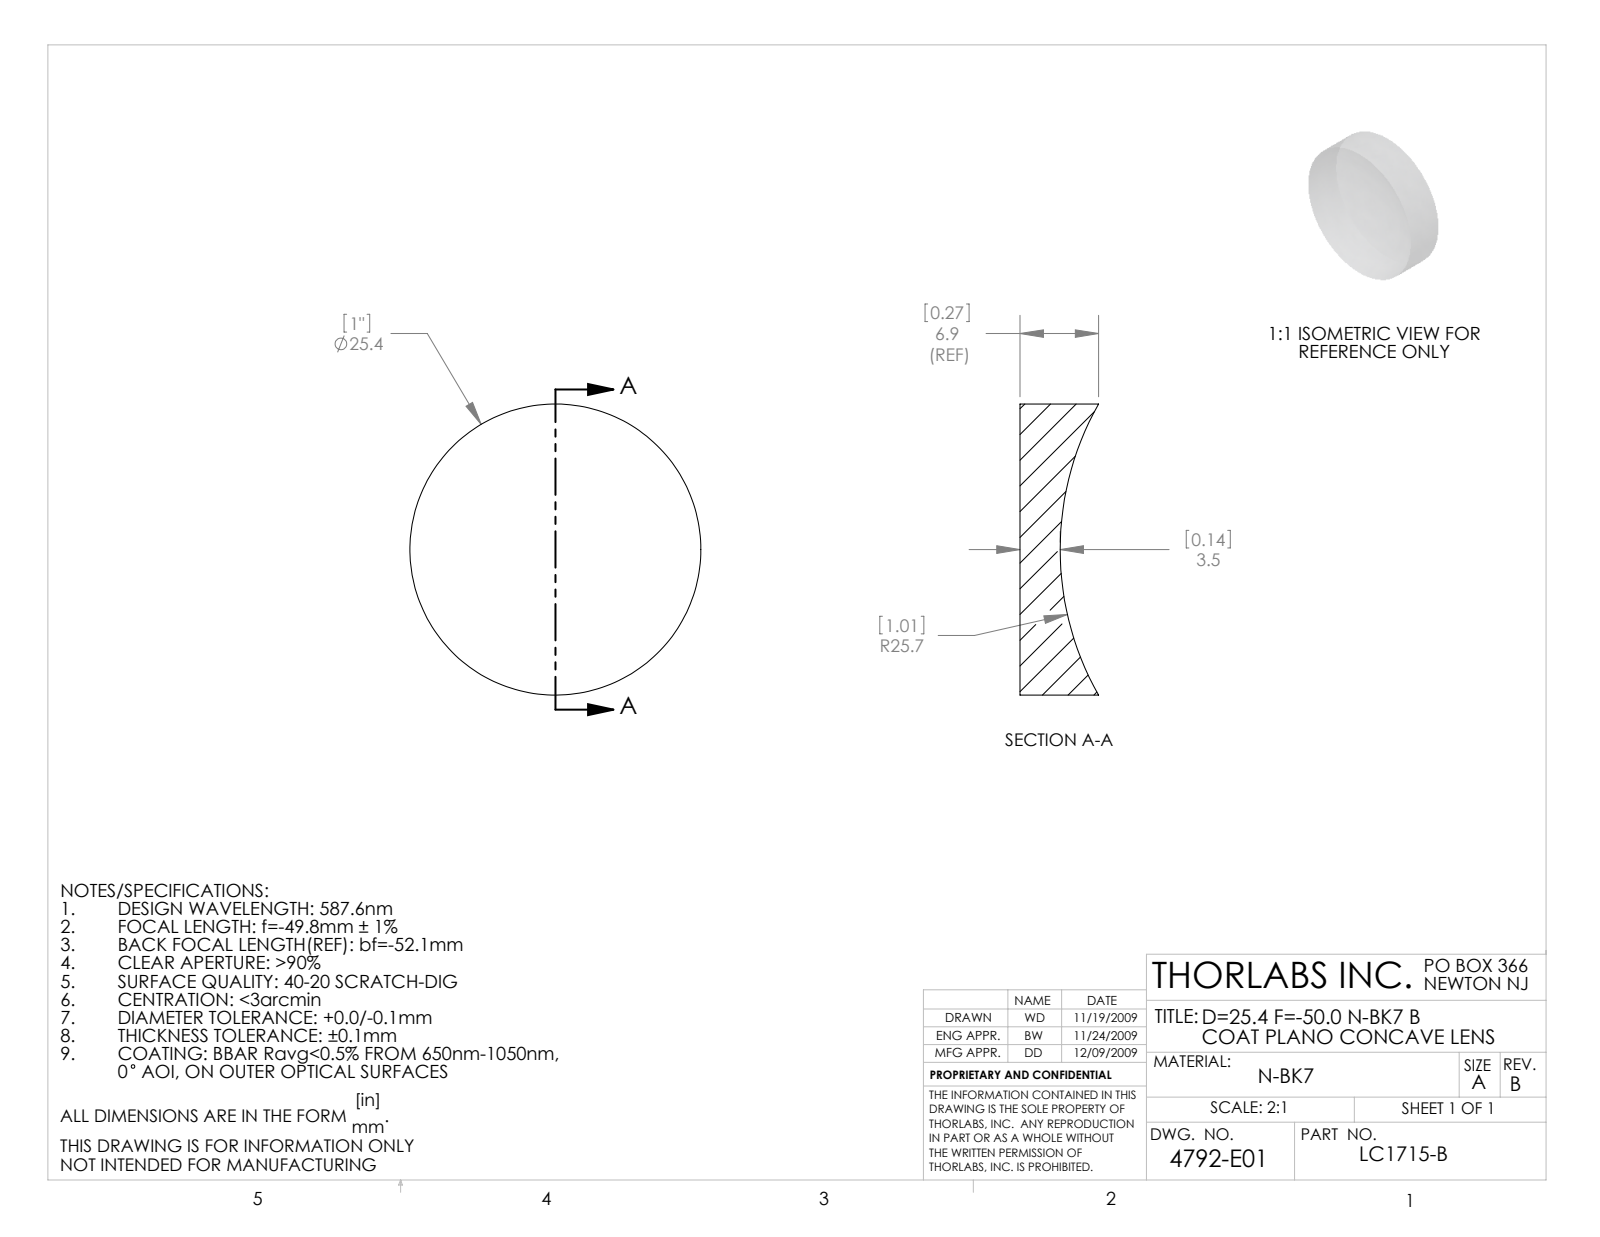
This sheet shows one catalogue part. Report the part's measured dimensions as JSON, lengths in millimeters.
{"part_name": "4792-E0W", "step_written_by": "SolidWorks 2009 (AUTOMOTIVE_DESIGN)", "units": "millimeters", "bodies": {"solids": 1, "faces": 5, "planar": 1, "cylindrical": 2, "other": 2}, "overall_size": [25.4, 25.4, 6.85], "volume_mm3": 2603, "surface_area_mm2": 1596, "round_bosses_or_shafts": [[25.4, 1]]}
